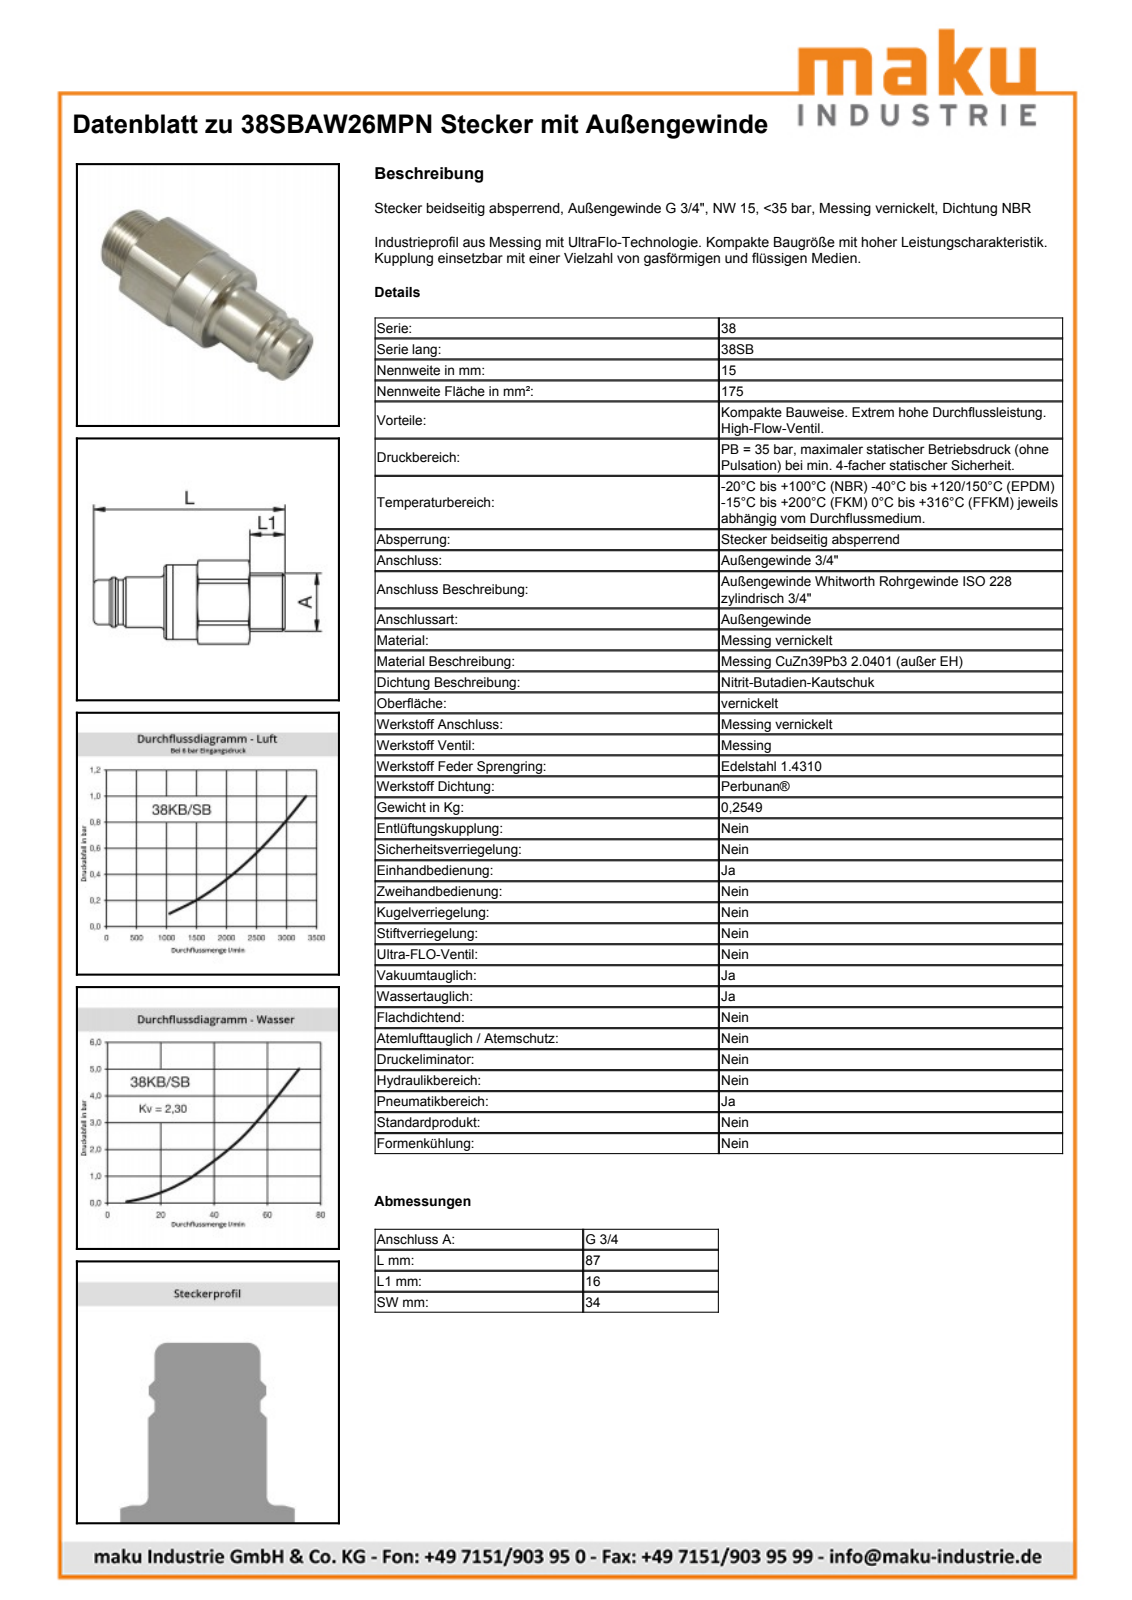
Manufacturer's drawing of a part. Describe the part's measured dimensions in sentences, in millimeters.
The part is named "D105999". Its 3-D file was written by "Autodesk Inventor 2011 (AUTOMOTIVE_DESIGN)". It is 1 solid with 57 faces: 14 planar, 18 cylindrical and 25 other. Overall it measures 87 by 37 by 34.88 millimeters. Its volume is 57 502 cubic millimeters and its surface area 11 226 square millimeters. Round holes: 1 of diameter 28.95. Round bosses or shafts: 1 of diameter 34, 1 of diameter 28.5, 1 of diameter 26.68, 1 of diameter 26.44, 1 of diameter 22.85, 1 of diameter 22.6, 1 of diameter 20.3. Partial cylindrical surfaces (rounded edges, fillets, slot ends): 1 of radius 18.5. The main face-to-face distances are 34, 16, 34.02, 38.9, 54.9, 32.1, 71, 87, 48.45, 16.35.
